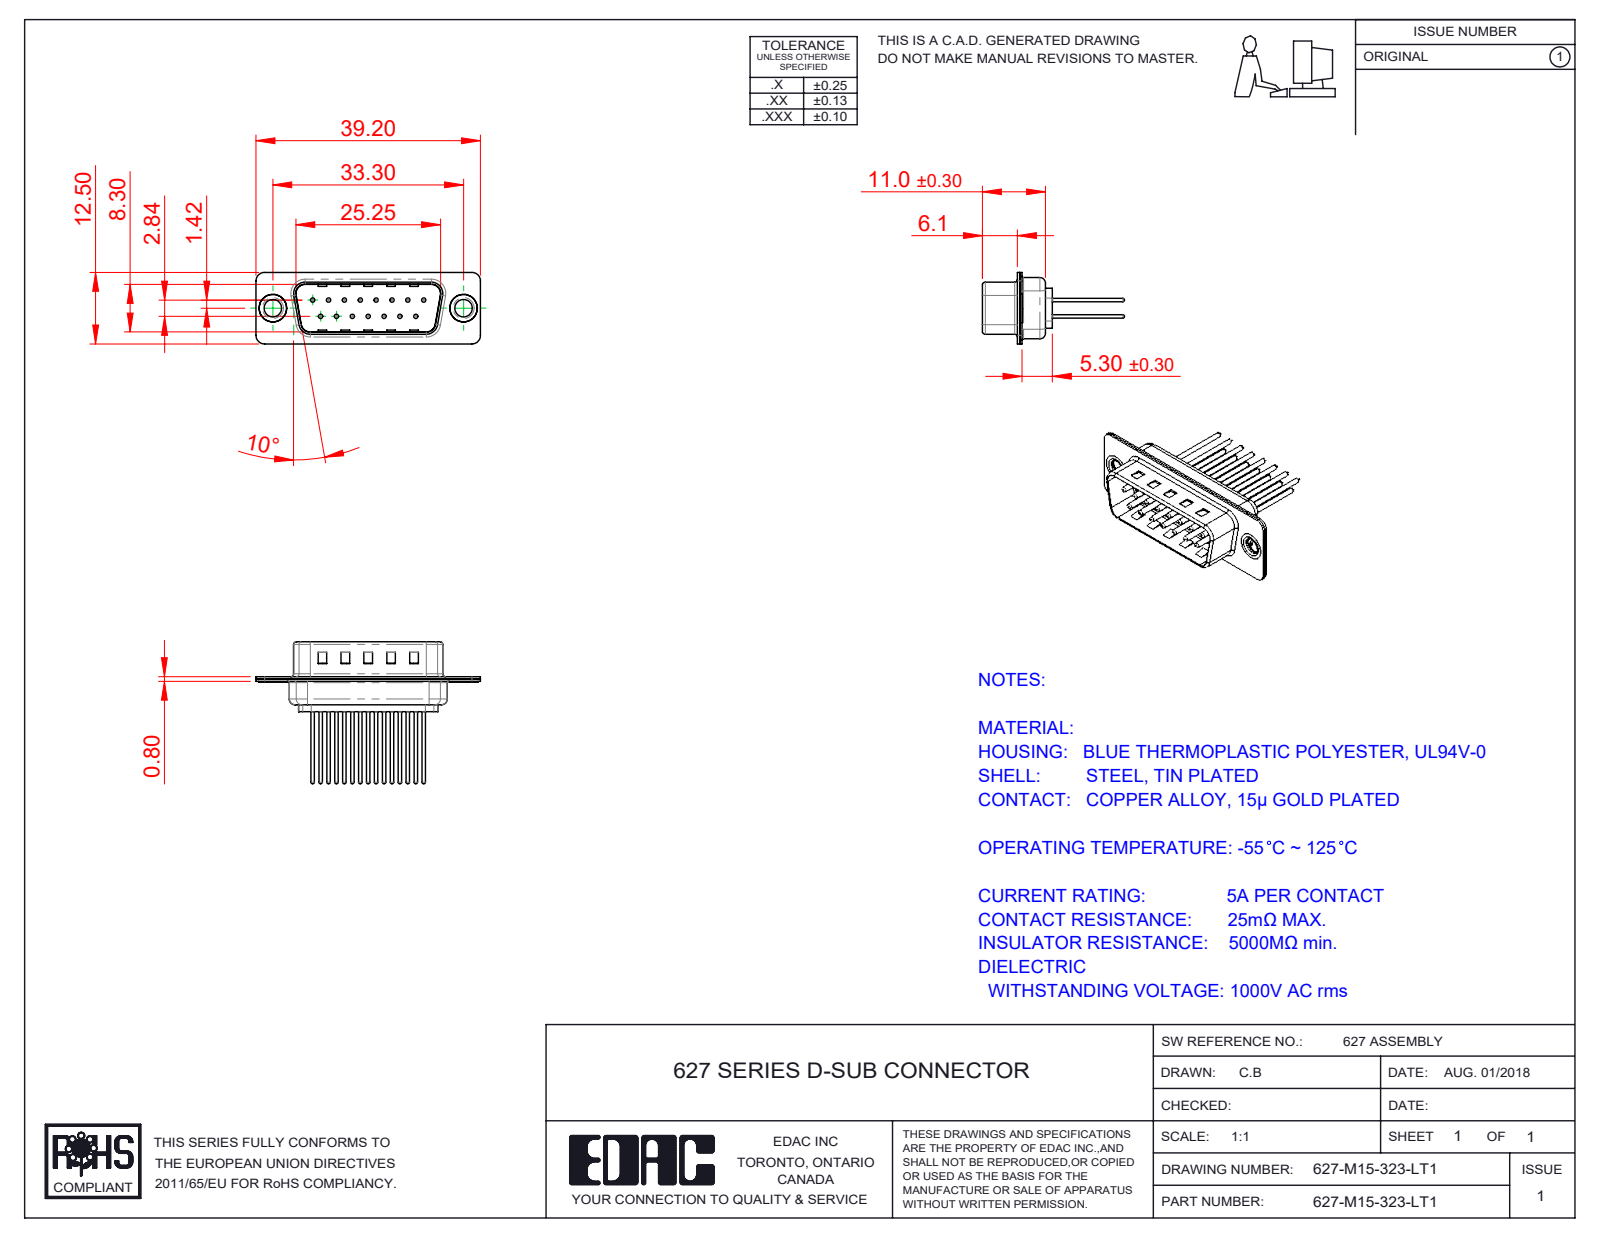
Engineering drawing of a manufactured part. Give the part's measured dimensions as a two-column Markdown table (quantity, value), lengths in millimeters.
| quantity | value |
| --- | --- |
| part name | 627M Shell Rear_15 Contacts; 627M Contact Row 1_23; 627M Contact Row 2_23; 627M Thru Hole Rivet (+3 more) |
| STEP written by | SolidWorks 2020 (CONFIG_CONTROL_DESIGN) |
| units | millimeters |
| bodies | 20 solids, 869 faces (244 planar, 327 cylindrical, 298 other) |
| overall size | 39.2 × 24.77 × 12.5 |
| volume | 1 794 mm³ |
| surface area | 4 857 mm² |
| round holes (diameter × count) | 0.75 × 15, 1.6 × 15, 2 × 15, 3.05 × 2, 4 × 2, 4.8 × 2 |
| round bosses / shafts (diameter × count) | 1.5 × 15, 0.6 × 15, 5 × 2, 4.9 × 2, 3.55 × 2 |
| partial cylindrical surfaces (radius × count) | 1.5 × 16, 2 × 12, 0.5 × 8, 1.6 × 8, 0.25 × 4, 0.6 × 4, 0.65 × 4, 0.9 × 4 |
| main face-to-face distances | 0.4, 0.8, 9.5, 9.1, 8.7, 9.9, 1.2, 6.1, 5.3, 5.7 |
| hole center spacings | 3.16, 2.77, 5.54, 8.31, 11.08, 5.03, 5.04, 7.48 |
